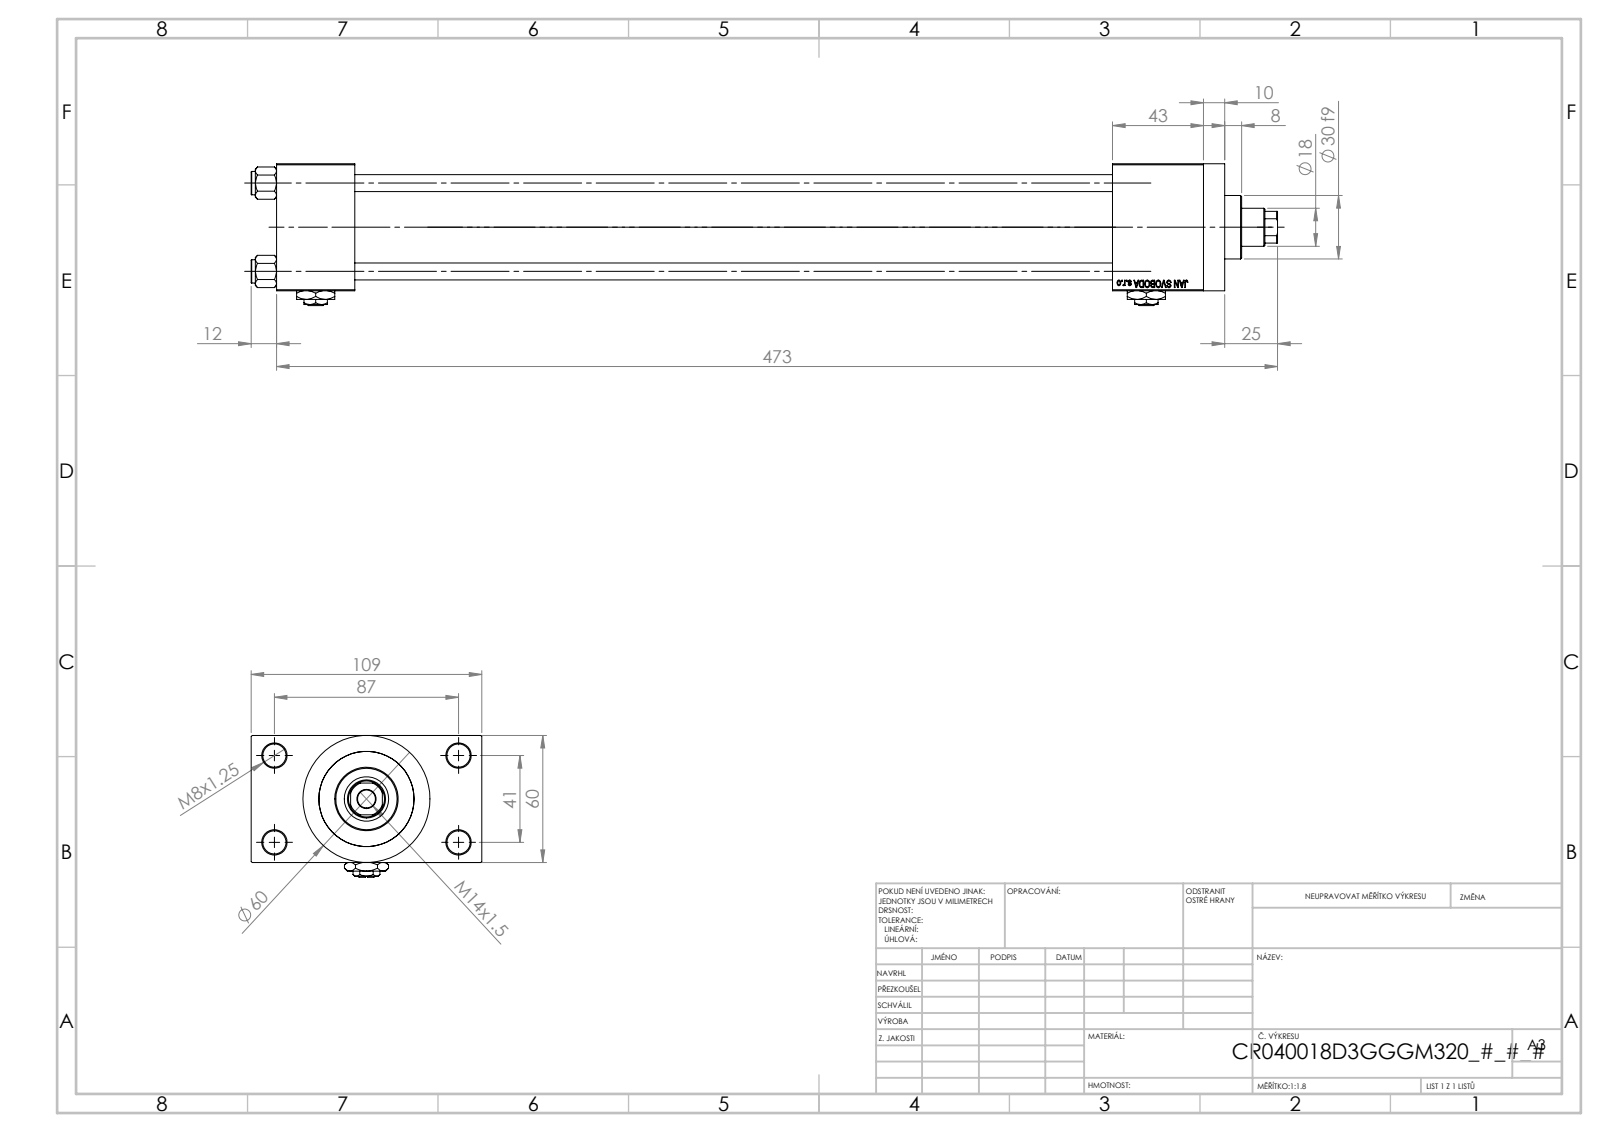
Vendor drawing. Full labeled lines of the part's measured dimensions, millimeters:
Part name (STEP PRODUCT): V215CR_D_TYCINKA; V215_VC_A; NUT_M5_D; V215CR_D_Body (+2 more)
STEP written by: SolidWorks 2019 (CONFIG_CONTROL_DESIGN)
Units: millimetres
Bodies: 13 solids, 1206 faces (546 planar, 100 cylindrical, 560 other)
Overall size (bounding box): 485 × 109 × 67
Volume: 773 830 mm³ · Surface area: 252 092 mm²
Round holes (diameter × count): ⌀8 ×4, ⌀11 ×4, ⌀7 ×2, ⌀16.66 ×2, ⌀24 ×2, ⌀8.5 ×1, ⌀18 ×1, ⌀21 ×1, ⌀31 ×1, ⌀40 ×1, ⌀45 ×1
Round bosses / shafts (diameter × count): ⌀11 ×4, ⌀60 ×1, ⌀46 ×1, ⌀30 ×1
Partial cylindrical surfaces — rounded edges, fillets, slot ends (radius × count): R8.5 ×1
Main face-to-face distances: 60, 24.5, 84.5, 358, 37, 395, 43, 438, 401, 109
Hole centre spacings: 22.65, 29.49, 41.7, 47.15, 48.09, 64.35, 76.49, 41
